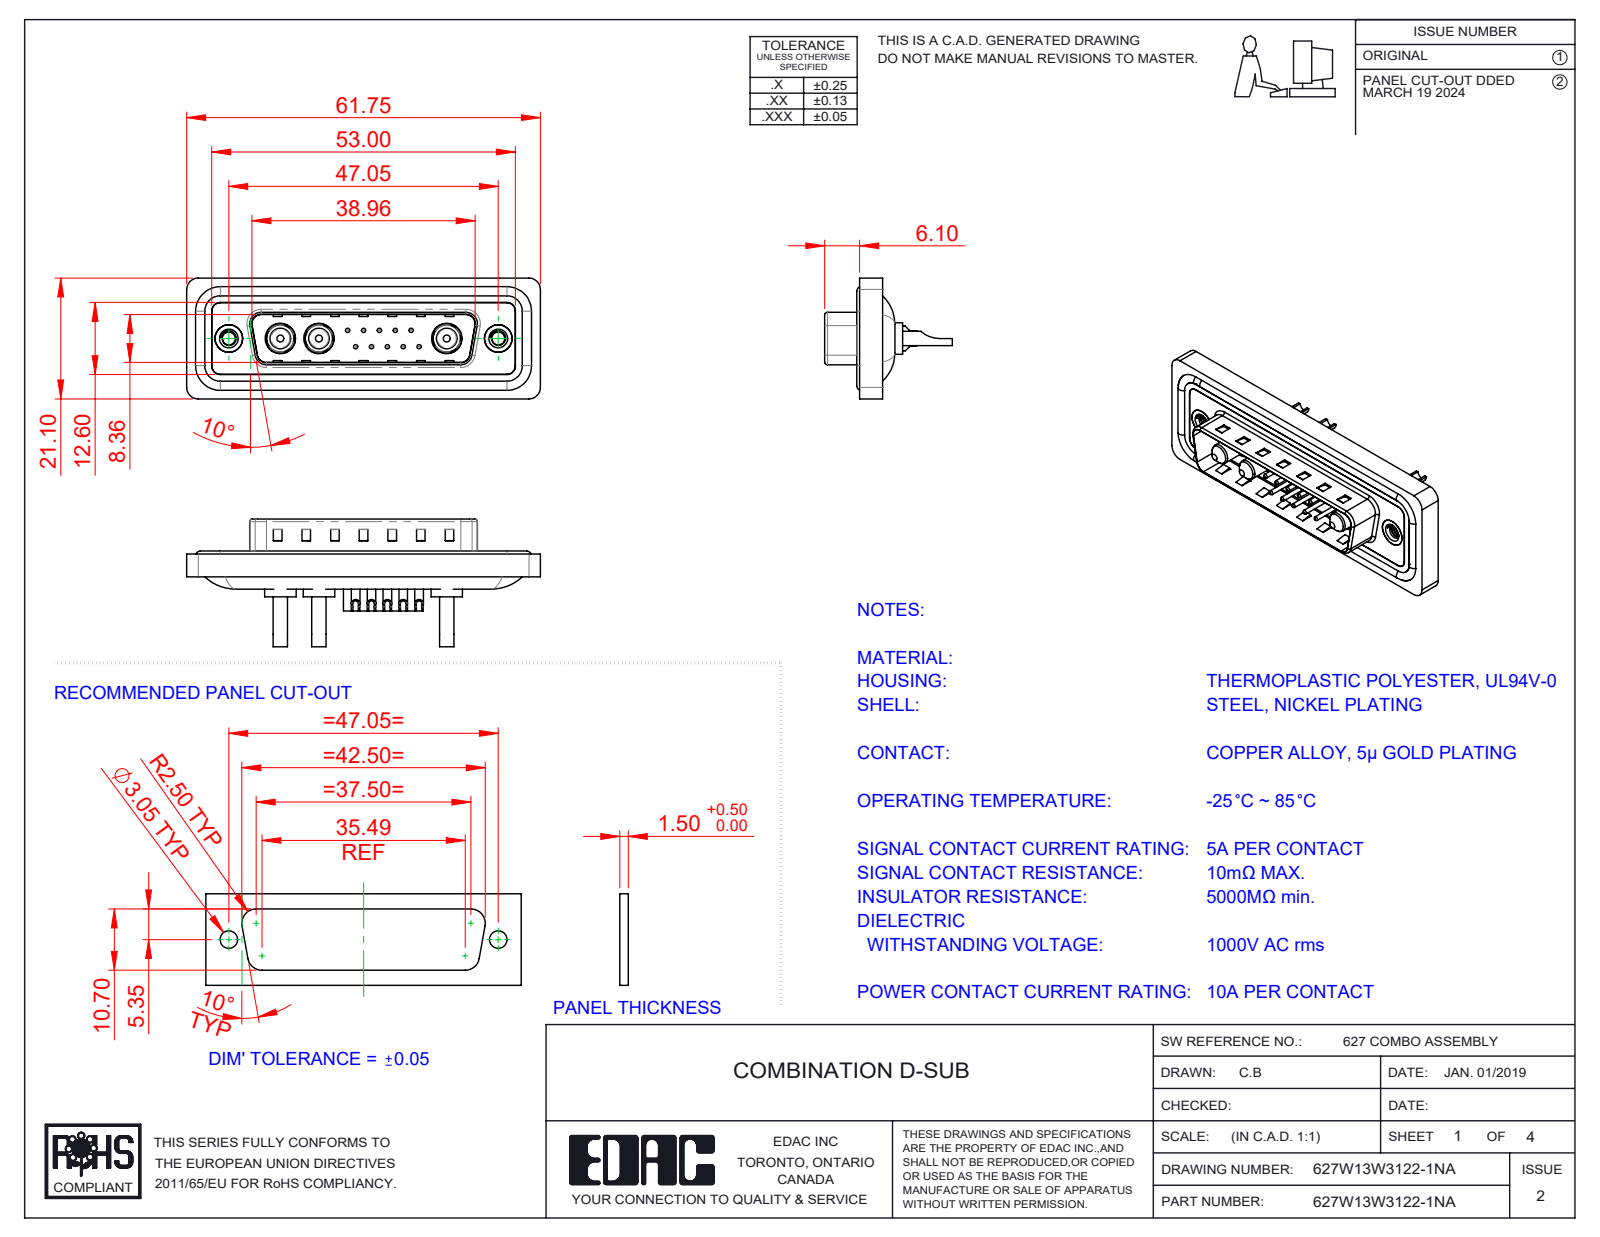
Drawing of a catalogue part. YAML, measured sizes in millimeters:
part_name: "627Combo Shell Rear_25 Contacts; 627W13W3122-1NA; Power Pin_10A SC; 627Combo Threaded Rivet_A (+5 more)"
step_written_by: "SolidWorks 2023 (CONFIG_CONTROL_DESIGN)"
units: millimeters
bodies: {solids: 23, faces: 983, planar: 335, cylindrical: 416, other: 232}
overall_size: [61.75, 22.3, 21.1]
volume: 7344
surface_area: 12095
round_holes:
  - {diameter: 0.75, count: 10}
  - {diameter: 1, count: 10}
  - {diameter: 1.6, count: 10}
  - {diameter: 2, count: 10}
  - {diameter: 1.7, count: 3}
  - {diameter: 4.85, count: 3}
  - {diameter: 5.3, count: 3}
  - {diameter: 2.26, count: 2}
  - {diameter: 4, count: 2}
  - {diameter: 4.8, count: 2}
  - {diameter: 5, count: 2}
round_bosses_or_shafts:
  - {diameter: 1.5, count: 10}
  - {diameter: 1.6, count: 4}
  - {diameter: 5.5, count: 3}
  - {diameter: 5.2, count: 3}
  - {diameter: 4.75, count: 3}
  - {diameter: 3.75, count: 3}
  - {diameter: 3.6, count: 3}
  - {diameter: 2.5, count: 3}
partial_cylinders:
  - {radius: 1.5, count: 22}
  - {radius: 2, count: 18}
  - {radius: 0.5, count: 8}
  - {radius: 1.6, count: 8}
  - {radius: 1, count: 6}
  - {radius: 0.25, count: 4}
  - {radius: 0.6, count: 4}
  - {radius: 0.65, count: 4}
face_to_face_distances: [0.4, 1.5, 1.1, 1.6, 0.5, 3.1, 2.9, 0.82, 9.58, 4.1]
hole_center_spacings: [3.16, 2.77, 5.04, 5.54, 7.49, 5.03, 8.31, 10.11]
